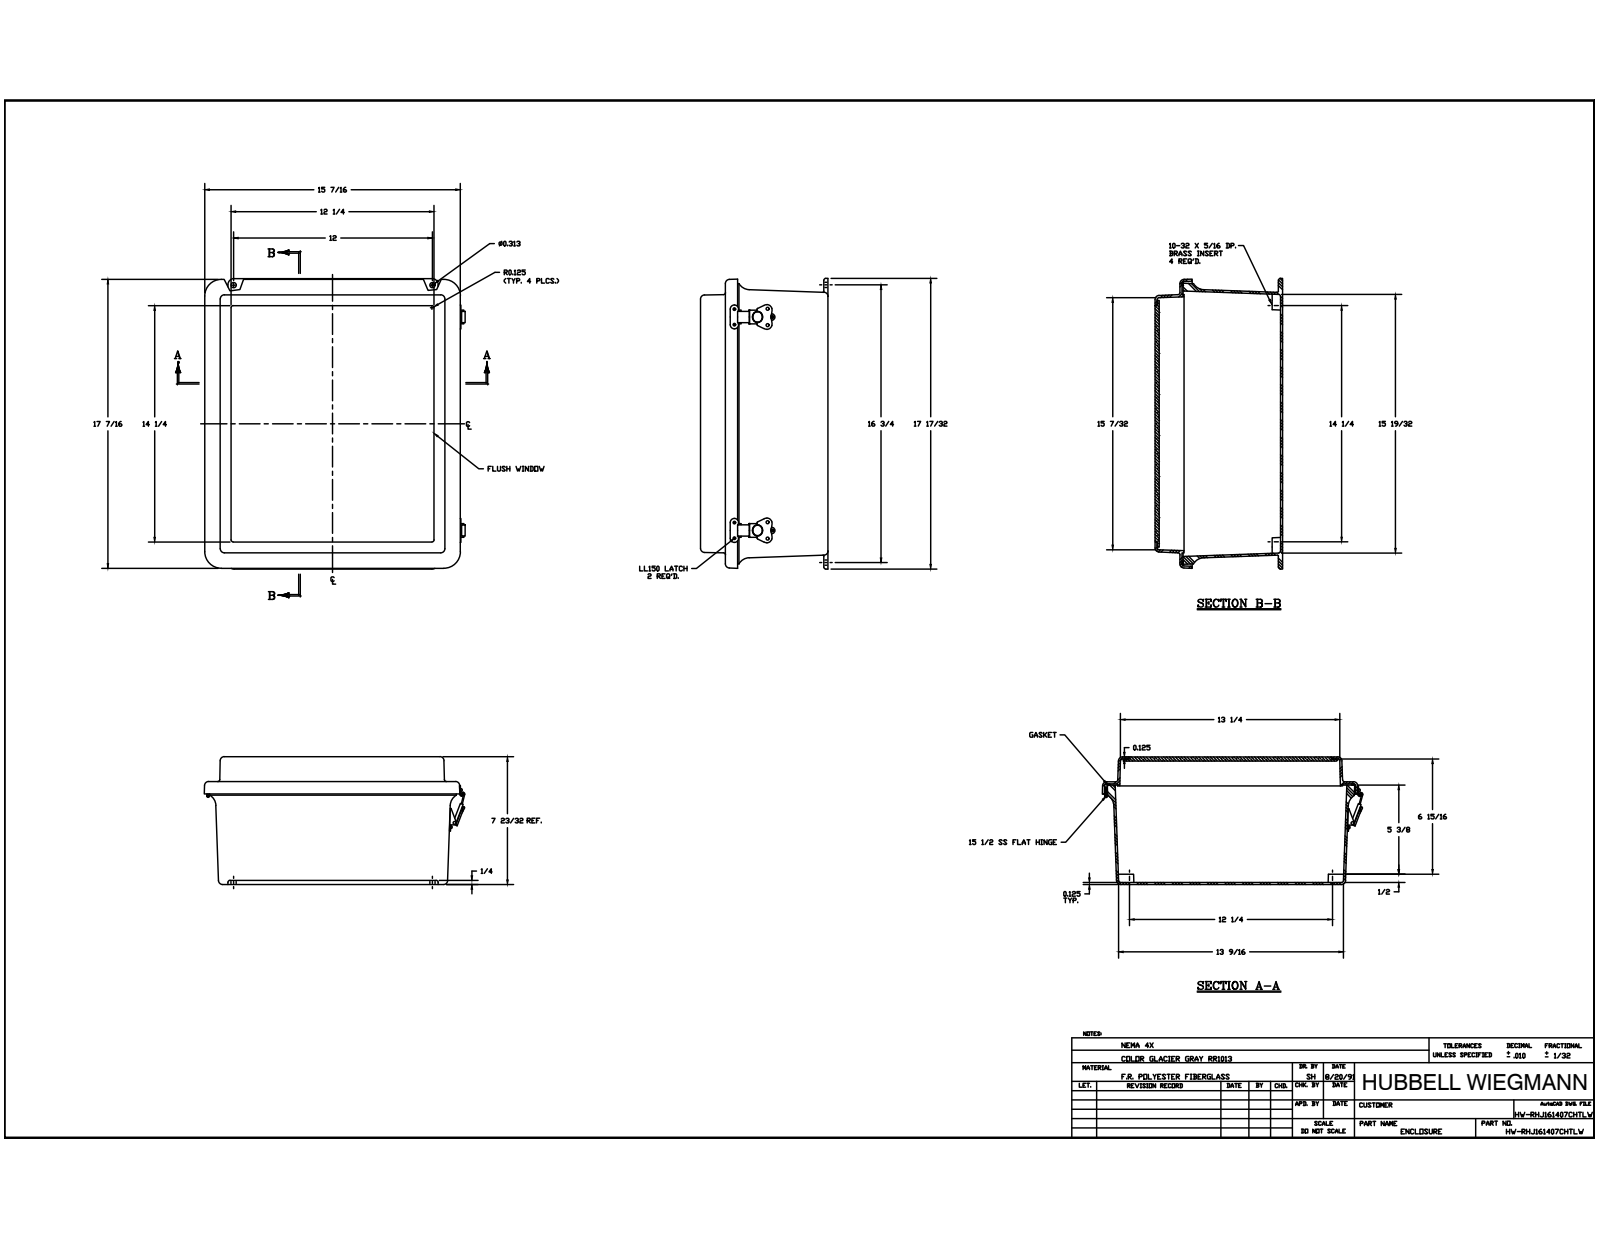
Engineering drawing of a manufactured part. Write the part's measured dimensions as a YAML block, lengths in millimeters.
part_name: "J1614HL_7; RMINS45821P_159; RMINS45821P_160; RMINS45821P_161 (+8 more)"
step_written_by: "Autodesk Inventor 2014 (AUTOMOTIVE_DESIGN)"
units: millimeters
bodies: {solids: 51, faces: 1346, planar: 609, cylindrical: 520, other: 217}
overall_size: [445.29, 396.87, 195.51]
volume: 2807000
surface_area: 1409000
round_holes:
  - {diameter: 3.56, count: 18}
  - {diameter: 3.33, count: 10}
  - {diameter: 3.86, count: 8}
  - {diameter: 3.3, count: 4}
  - {diameter: 3.96, count: 4}
  - {diameter: 4.2, count: 4}
  - {diameter: 5, count: 4}
  - {diameter: 5.54, count: 4}
  - {diameter: 3, count: 2}
  - {diameter: 3.5, count: 2}
  - {diameter: 4.61, count: 2}
  - {diameter: 4.62, count: 2}
round_bosses_or_shafts:
  - {diameter: 6.35, count: 18}
  - {diameter: 3.17, count: 18}
  - {diameter: 6.86, count: 4}
  - {diameter: 14.8, count: 2}
  - {diameter: 13.3, count: 2}
  - {diameter: 5.3, count: 2}
  - {diameter: 4.7, count: 2}
  - {diameter: 3.25, count: 2}
partial_cylinders:
  - {radius: 3.17, count: 24}
  - {radius: 0.79, count: 20}
  - {radius: 6.35, count: 20}
  - {radius: 2, count: 19}
  - {radius: 0.95, count: 8}
  - {radius: 1, count: 8}
  - {radius: 1.15, count: 8}
  - {radius: 1.2, count: 8}
face_to_face_distances: [3.18, 189.16, 3.17, 6.35, 195.51, 192.33, 185.98, 151.01, 38.15, 154.19]
hole_center_spacings: [95.25, 190.5, 326.84, 285.75, 326.86, 6.35, 88.9, 23.82]
